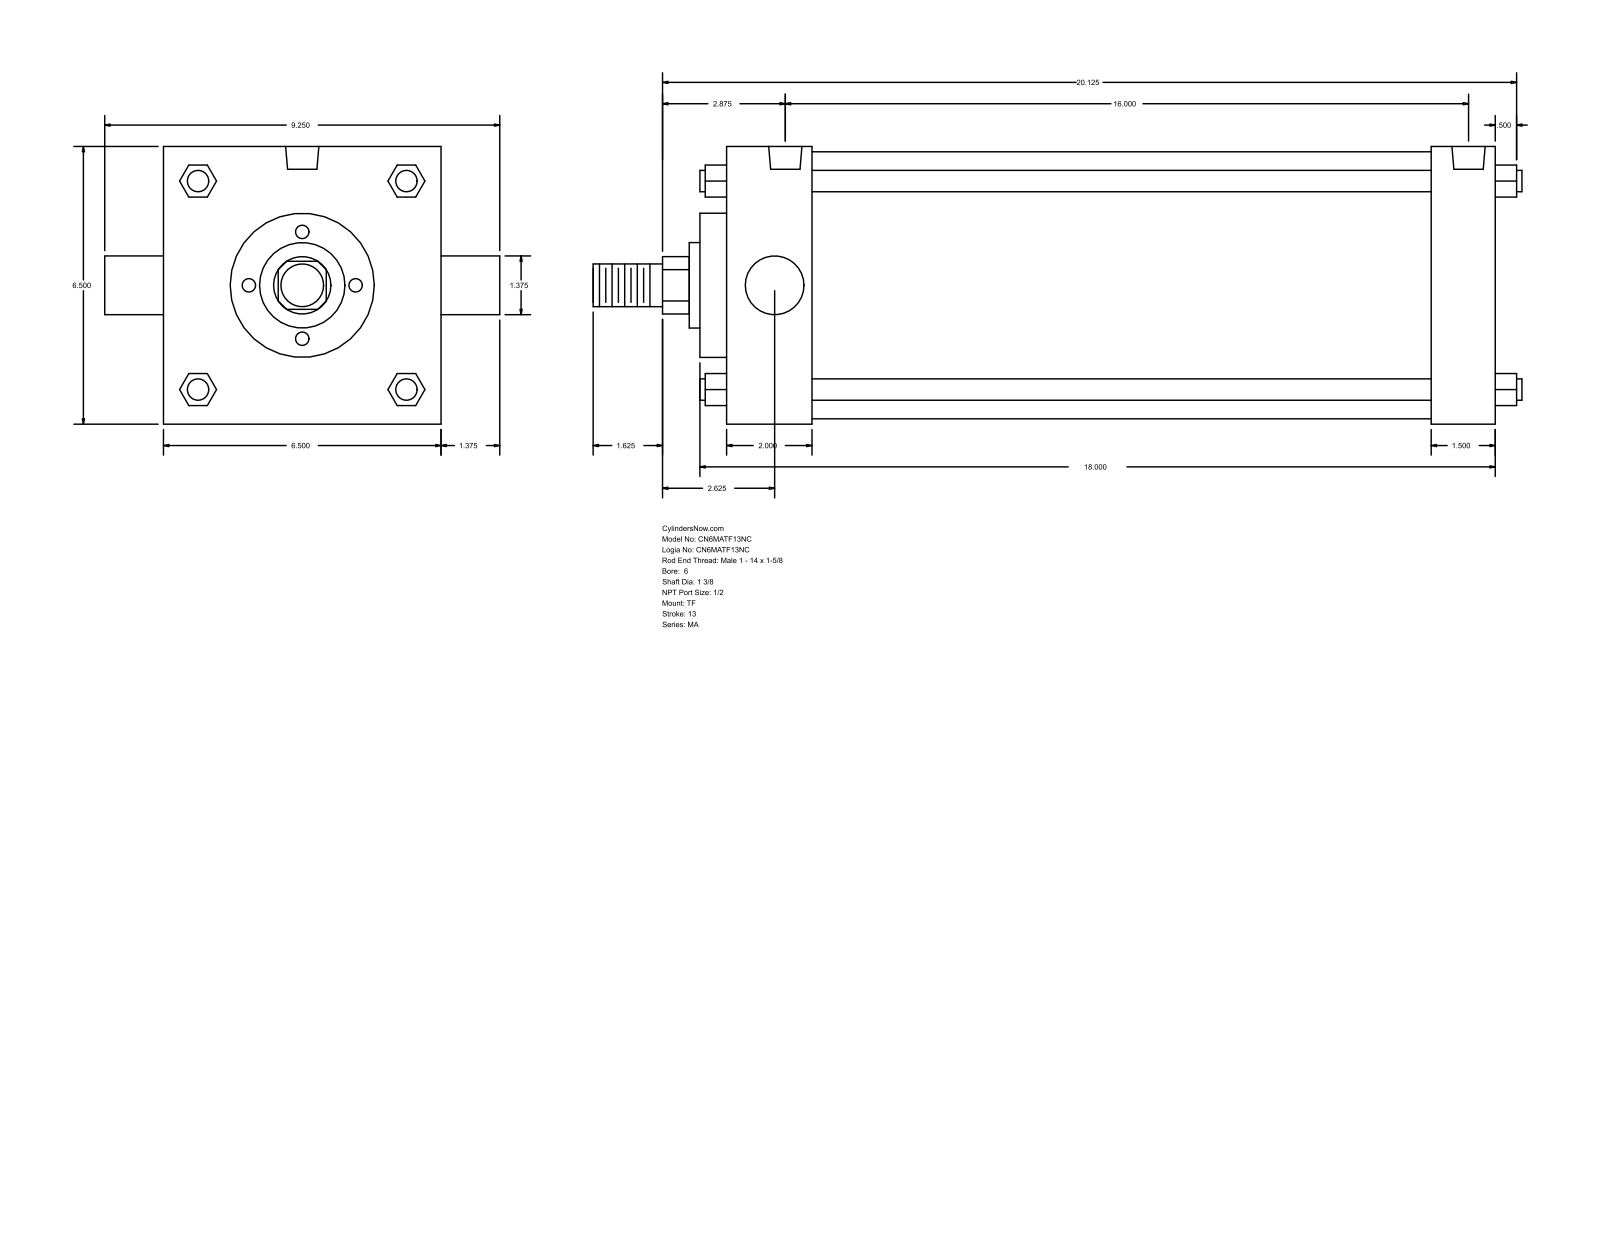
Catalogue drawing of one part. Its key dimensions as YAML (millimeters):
part_name: "MA_TF__0600_1.375"
step_written_by: "GSSL Pune (CONFIG_CONTROL_DESIGN)"
units: millimeters
bodies: {solids: 0, faces: 122, planar: 93, cylindrical: 29, other: 0}
overall_size: [552.45, 234.95, 165.1]
round_holes:
  - {diameter: 17.46, count: 3}
  - {diameter: 19.77, count: 2}
round_bosses_or_shafts:
  - {diameter: 12.7, count: 4}
  - {diameter: 34.92, count: 2}
  - {diameter: 158.75, count: 1}
  - {diameter: 85.72, count: 1}
  - {diameter: 50.8, count: 1}
  - {diameter: 25.4, count: 1}
partial_cylinders:
  - {radius: 17.06, count: 1}
face_to_face_distances: [165.1, 460.38, 50.8, 422.28, 38.1, 409.58, 371.48, 66.67, 15.87, 438.15]
hole_center_spacings: [3.18, 406.4, 409.58]
